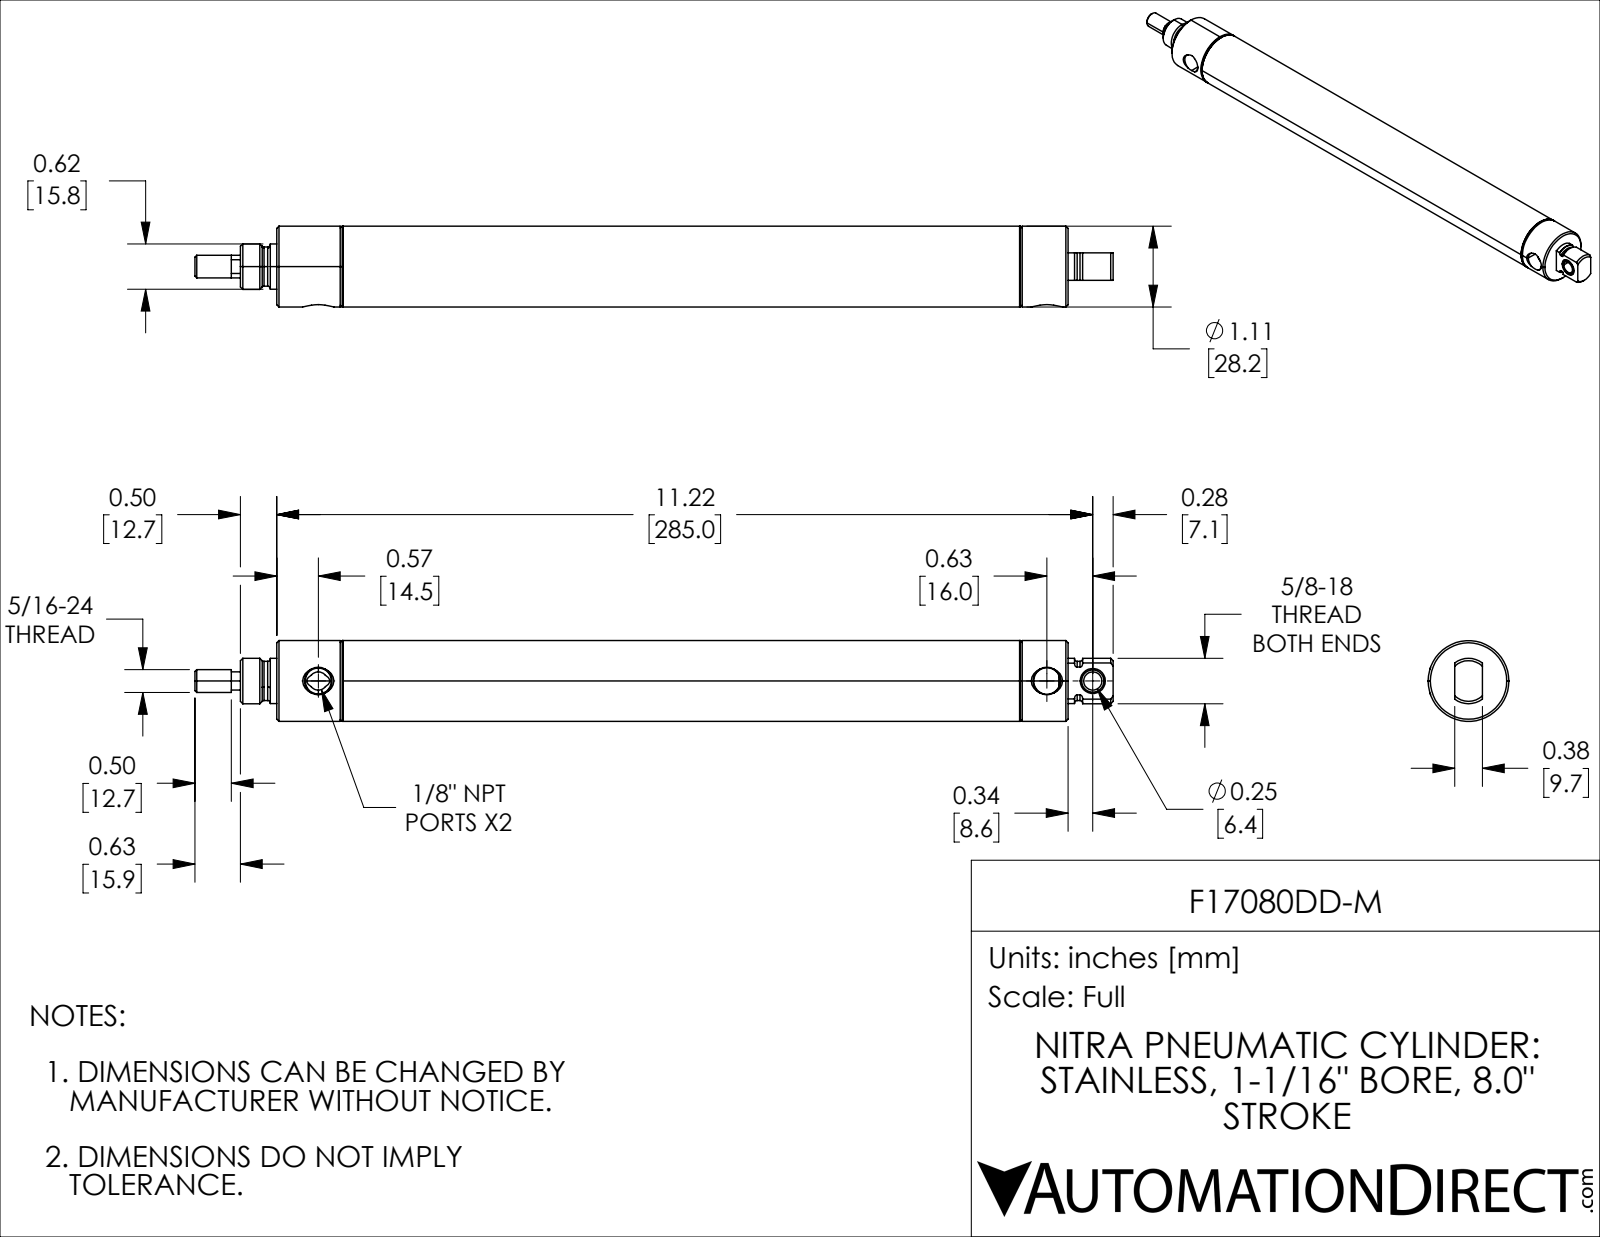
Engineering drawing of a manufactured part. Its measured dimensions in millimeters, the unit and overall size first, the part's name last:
Units: millimetres
Overall size (bounding box): 320.68 × 28.19 × 28.19
Round holes (diameter × count): ⌀6.38 ×1, ⌀8.53 ×1, ⌀8.78 ×1, ⌀9.25 ×1, ⌀9.53 ×1, ⌀19.05 ×1, ⌀25.7 ×1
Round bosses / shafts (diameter × count): ⌀28.19 ×1, ⌀27.23 ×1, ⌀15.88 ×1, ⌀15.81 ×1, ⌀13.68 ×1, ⌀7.94 ×1, ⌀7.92 ×1
Partial cylindrical surfaces — rounded edges, fillets, slot ends (radius × count): R3.17 ×1, R6.84 ×1
Main face-to-face distances: 22.22, 203.2, 225.42, 247.75, 44.55, 22.33, 28.58, 231.78, 254, 276.33
Hole centre spacings: 16.01
Volume: 64 413 mm³ · Surface area: 62 580 mm²
Bodies: 5 solids, 156 faces (30 planar, 58 cylindrical, 68 other)
Part name (STEP PRODUCT): F17080DD-M_5; F17080DD-M_3; F17080DD-M; F17080DD-M_7 (+2 more)
STEP written by: SolidWorks 2021 (CONFIG_CONTROL_DESIGN)
